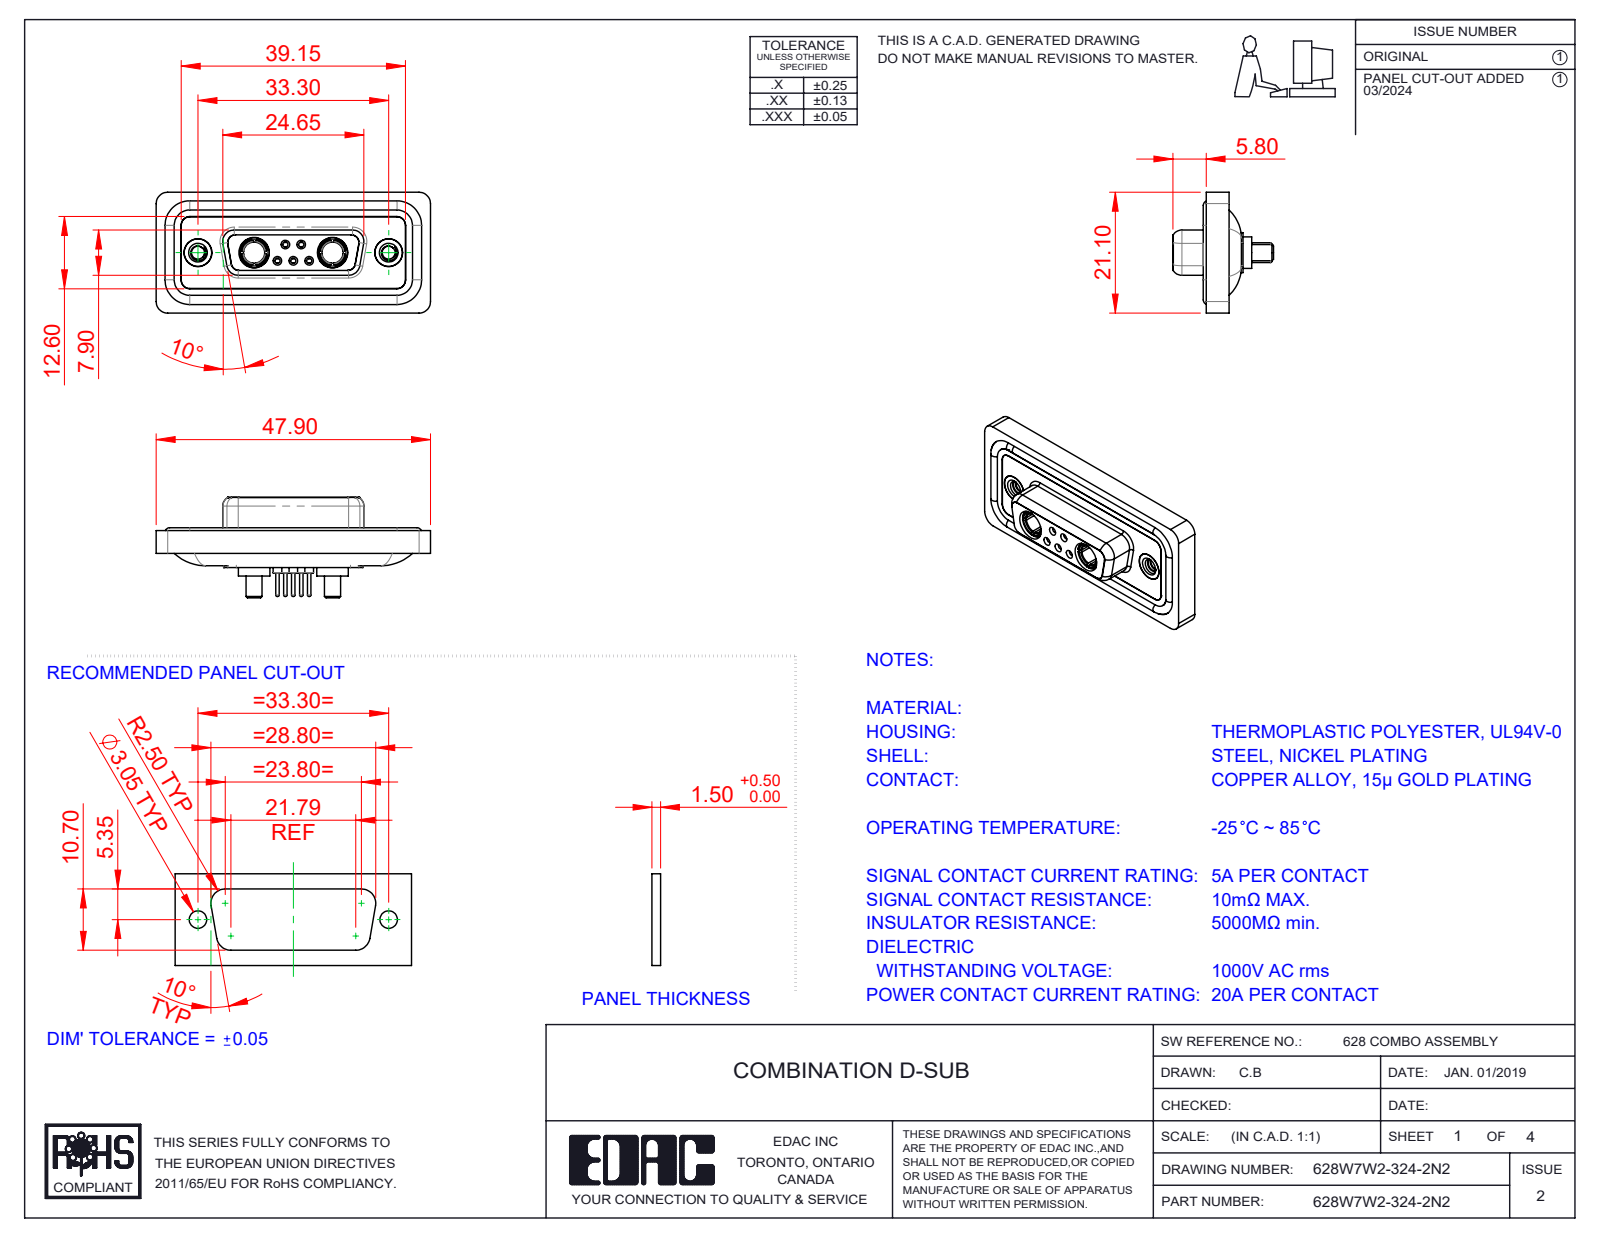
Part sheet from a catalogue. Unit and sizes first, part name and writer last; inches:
Units: inches
Overall size (bounding box): 1.886 × 0.831 × 0.691
Round holes (diameter × count): ⌀0.035 ×5, ⌀0.043 ×5, ⌀0.059 ×5, ⌀0.079 ×5, ⌀0.191 ×4, ⌀0.063 ×3, ⌀0.067 ×2, ⌀0.089 ×2, ⌀0.146 ×2, ⌀0.157 ×2, ⌀0.159 ×2, ⌀0.197 ×2
Round bosses / shafts (diameter × count): ⌀0.063 ×6, ⌀0.087 ×5, ⌀0.024 ×5, ⌀0.217 ×2, ⌀0.205 ×2, ⌀0.195 ×2, ⌀0.195 ×2, ⌀0.189 ×2
Partial cylindrical surfaces — rounded edges, fillets, slot ends (radius × count): R0.059 ×22, R0.079 ×20, R0.053 ×12, R0.063 ×8, R0.01 ×4, R0.02 ×4, R0.024 ×4, R0.026 ×4
Main face-to-face distances: 0.016, 0.071, 0.063, 0.02, 0.114, 0.293, 0.043, 0.222, 0.26, 0.278
Hole centre spacings: 0.124, 0.109, 0.386, 0.925, 0.17, 0.17, 0.198, 0.198
Volume: 0.371 in³ · Surface area: 15.32 in²
Bodies: 16 solids, 809 faces (238 planar, 329 cylindrical, 242 other)
Part name (STEP PRODUCT): 628W7W2-324-2N2; 628Combo Housing_7W2; 628Combo Contact Row 2_24; 628Combo Threaded Rivet_2 (+5 more)
STEP written by: SolidWorks 2023 (CONFIG_CONTROL_DESIGN)
